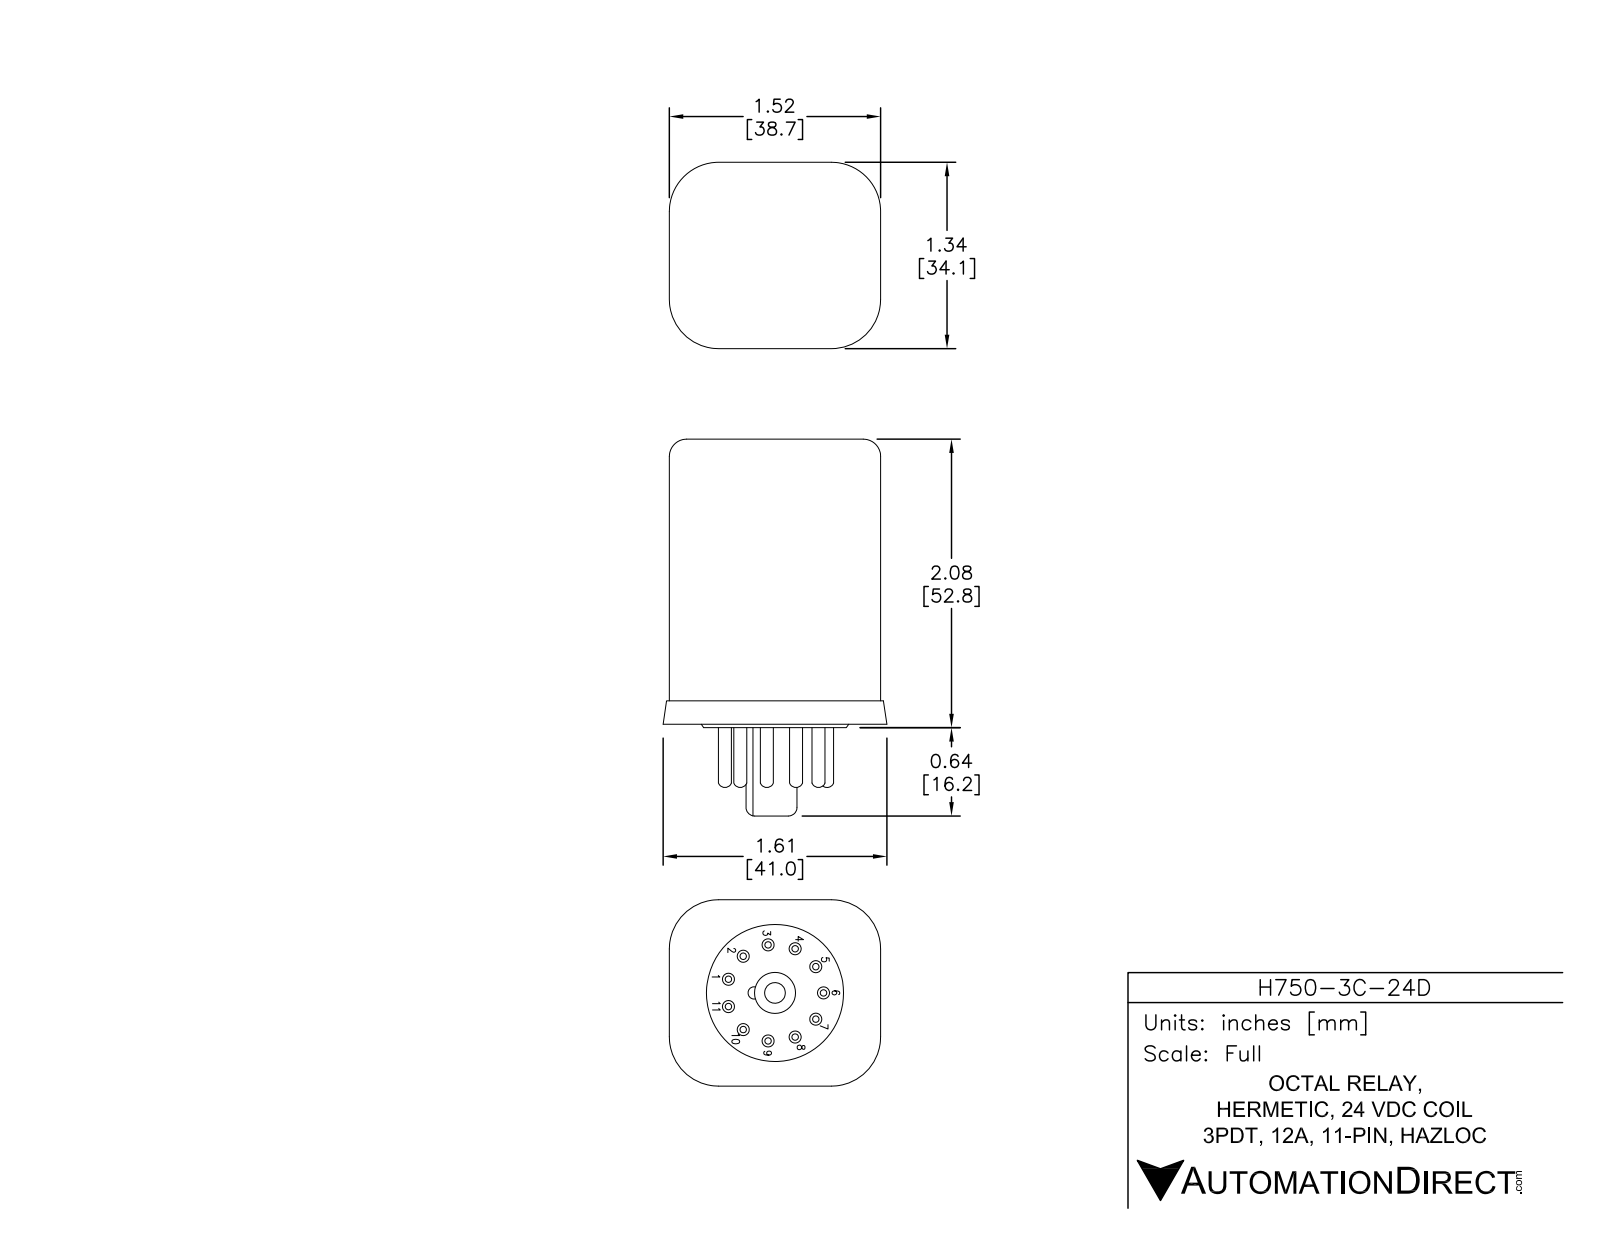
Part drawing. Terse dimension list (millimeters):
name: H750-3C-24D
written by: SolidWorks 2013 (AUTOMOTIVE_DESIGN)
unit: mm
bodies: 1 solid, 280 faces (117 planar, 65 cylindrical, 98 other)
size: 67.3 × 41.35 × 36.6
volume: 66 961 mm³; area: 10 714 mm²
holes: 8× ⌀4.5, 1× ⌀3.9
bosses: 8× ⌀2.31, 1× ⌀27, 1× ⌀12, 1× ⌀8
rounds: 8× R0.62, 4× R2.5, 4× R10, 4× R11.3, 2× R0.5, 1× R0.59
face distances: 53, 34, 38.75, 0.5, 53.5, 1.3, 35.3, 40.05, 1, 54
hole spacings: 8.5, 12.02, 15.7, 6.5, 6.51, 16.99
